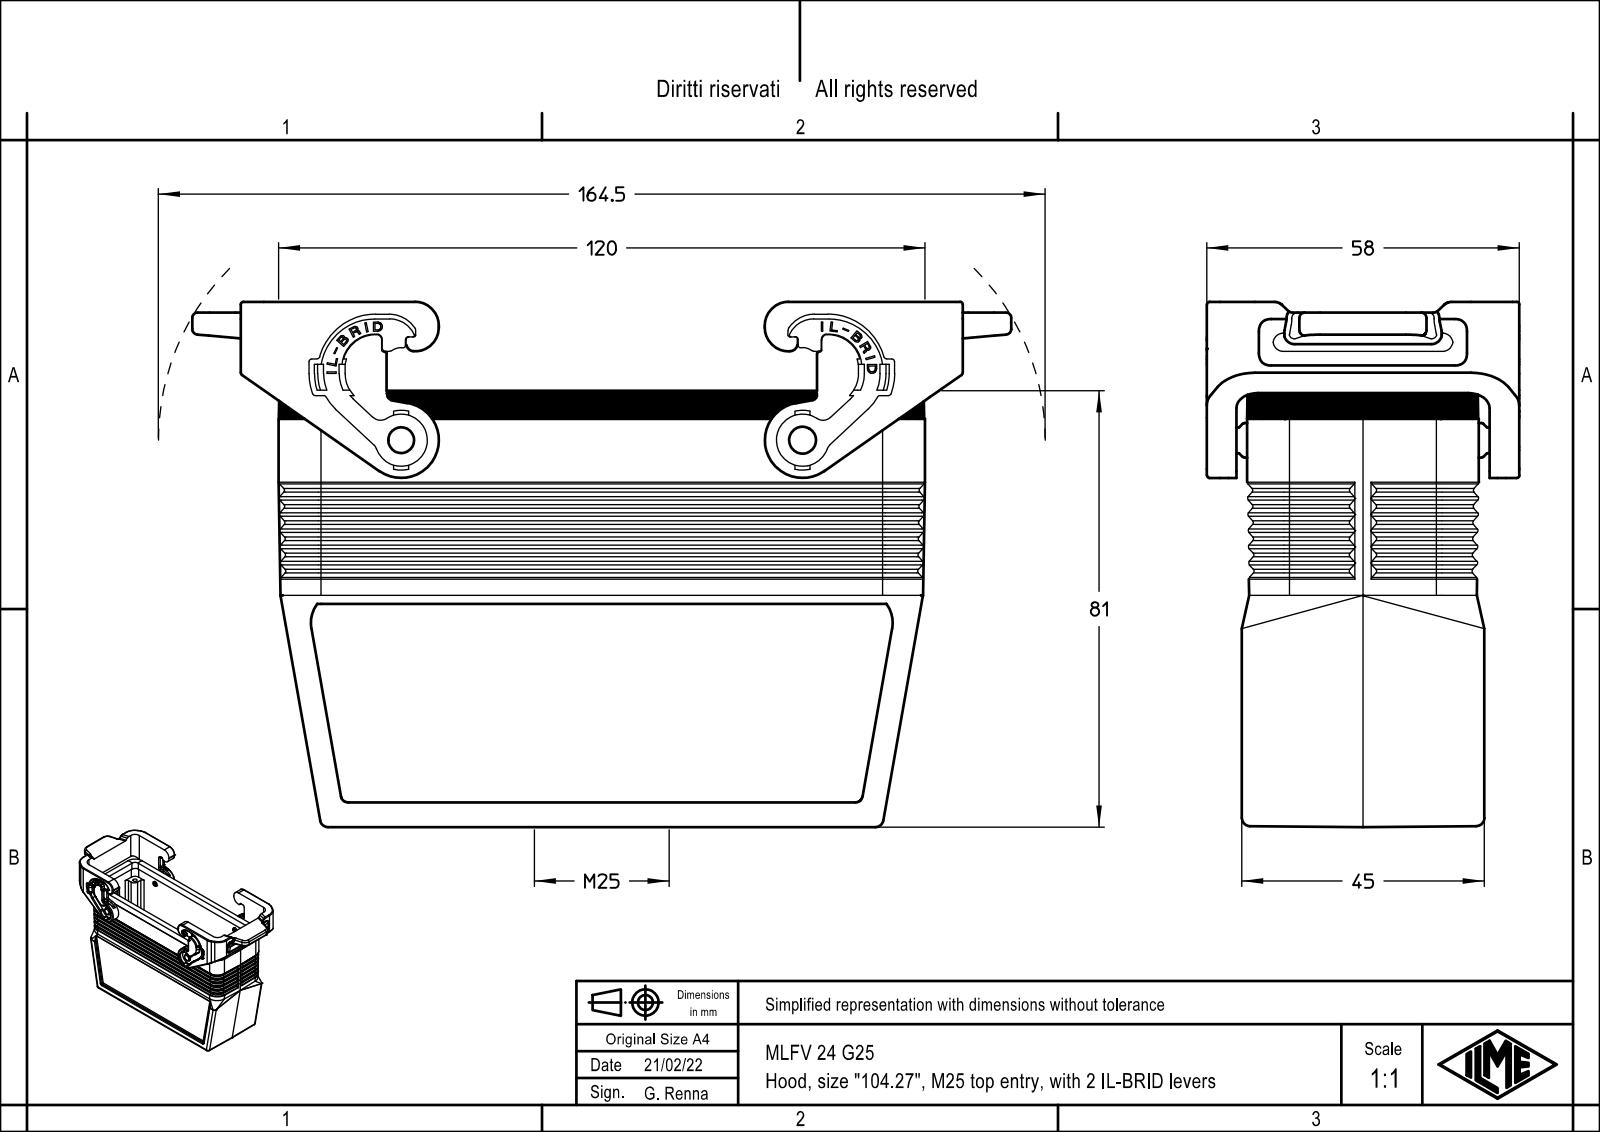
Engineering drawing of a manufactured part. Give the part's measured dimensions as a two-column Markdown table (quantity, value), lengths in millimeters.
| quantity | value |
| --- | --- |
| part name | MLFV_24_G25 |
| STEP written by | Creo Elements/Direct Modeling 20.1B 02-Apr-2019 (C) Parametric Technology GmbH (AUTOMOTIVE_DESIGN) |
| units | millimeters |
| bodies | 1 solid, 1599 faces (1028 planar, 391 cylindrical, 180 other) |
| overall size | 152 × 97.45 × 58 |
| volume | 139 692 mm³ |
| surface area | 72 343 mm² |
| round holes (diameter × count) | 2.75 × 4, 23.6 × 1 |
| round bosses / shafts (diameter × count) | 6.8 × 2, 4.8 × 2 |
| partial cylindrical surfaces (radius × count) | 0.5 × 104, 1 × 46, 3 × 20, 7 × 16, 0.33 × 15, 1.5 × 14, 0.3 × 8, 2 × 8 |
| main face-to-face distances | 39.25, 3.75, 2, 1, 4.75, 43, 5.75, 34.5, 38.25, 35.5 |
| hole center spacings | 53.72, 27, 104, 107.45 |
